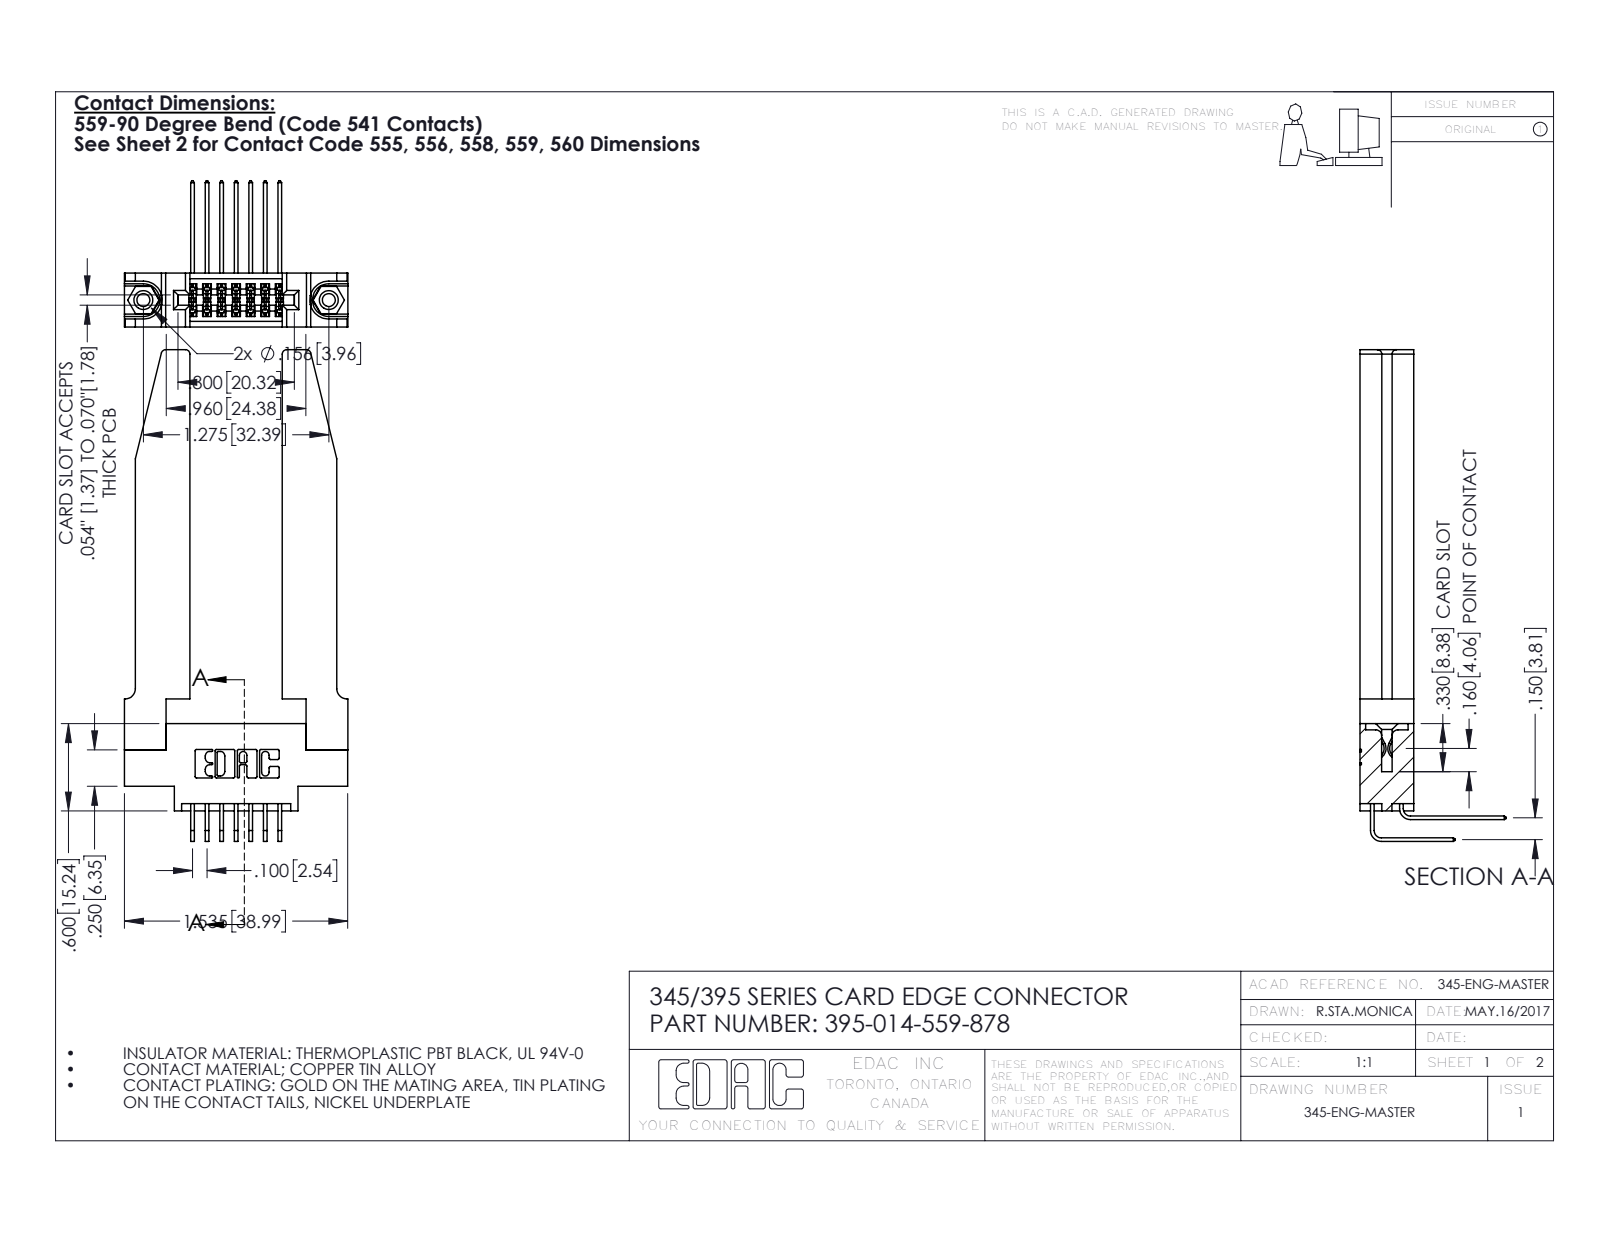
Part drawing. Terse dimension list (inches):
name: 345-220-078_345-220-078; 395-014-559-878; 345 Part_0.170 Offset - 0.156 Dia-TH; 345-292-001_558 559 Tail - 1 (+2 more)
written by: SolidWorks 2016 (CONFIG_CONTROL_DESIGN)
unit: in
bodies: 19 solids, 1092 faces (716 planar, 324 cylindrical, 52 other)
size: 3.379 × 1.536 × 1.005
volume: 0.684 in³; area: 18.22 in²
holes: 2× ⌀0.089, 2× ⌀0.125, 2× ⌀0.156, 1× ⌀0.064
bosses: 2× ⌀0.155
rounds: 22× R0.006, 22× R0.01, 8× R0.03, 6× R0.007, 6× R0.031, 3× R0.026, 2× R0.014, 2× R0.019
face distances: 0.37, 0.15, 0.072, 0.148, 0.22, 0.298, 0.077, 0.635, 0.095, 0.2
hole spacings: 0.27, 1.045, 1.275
